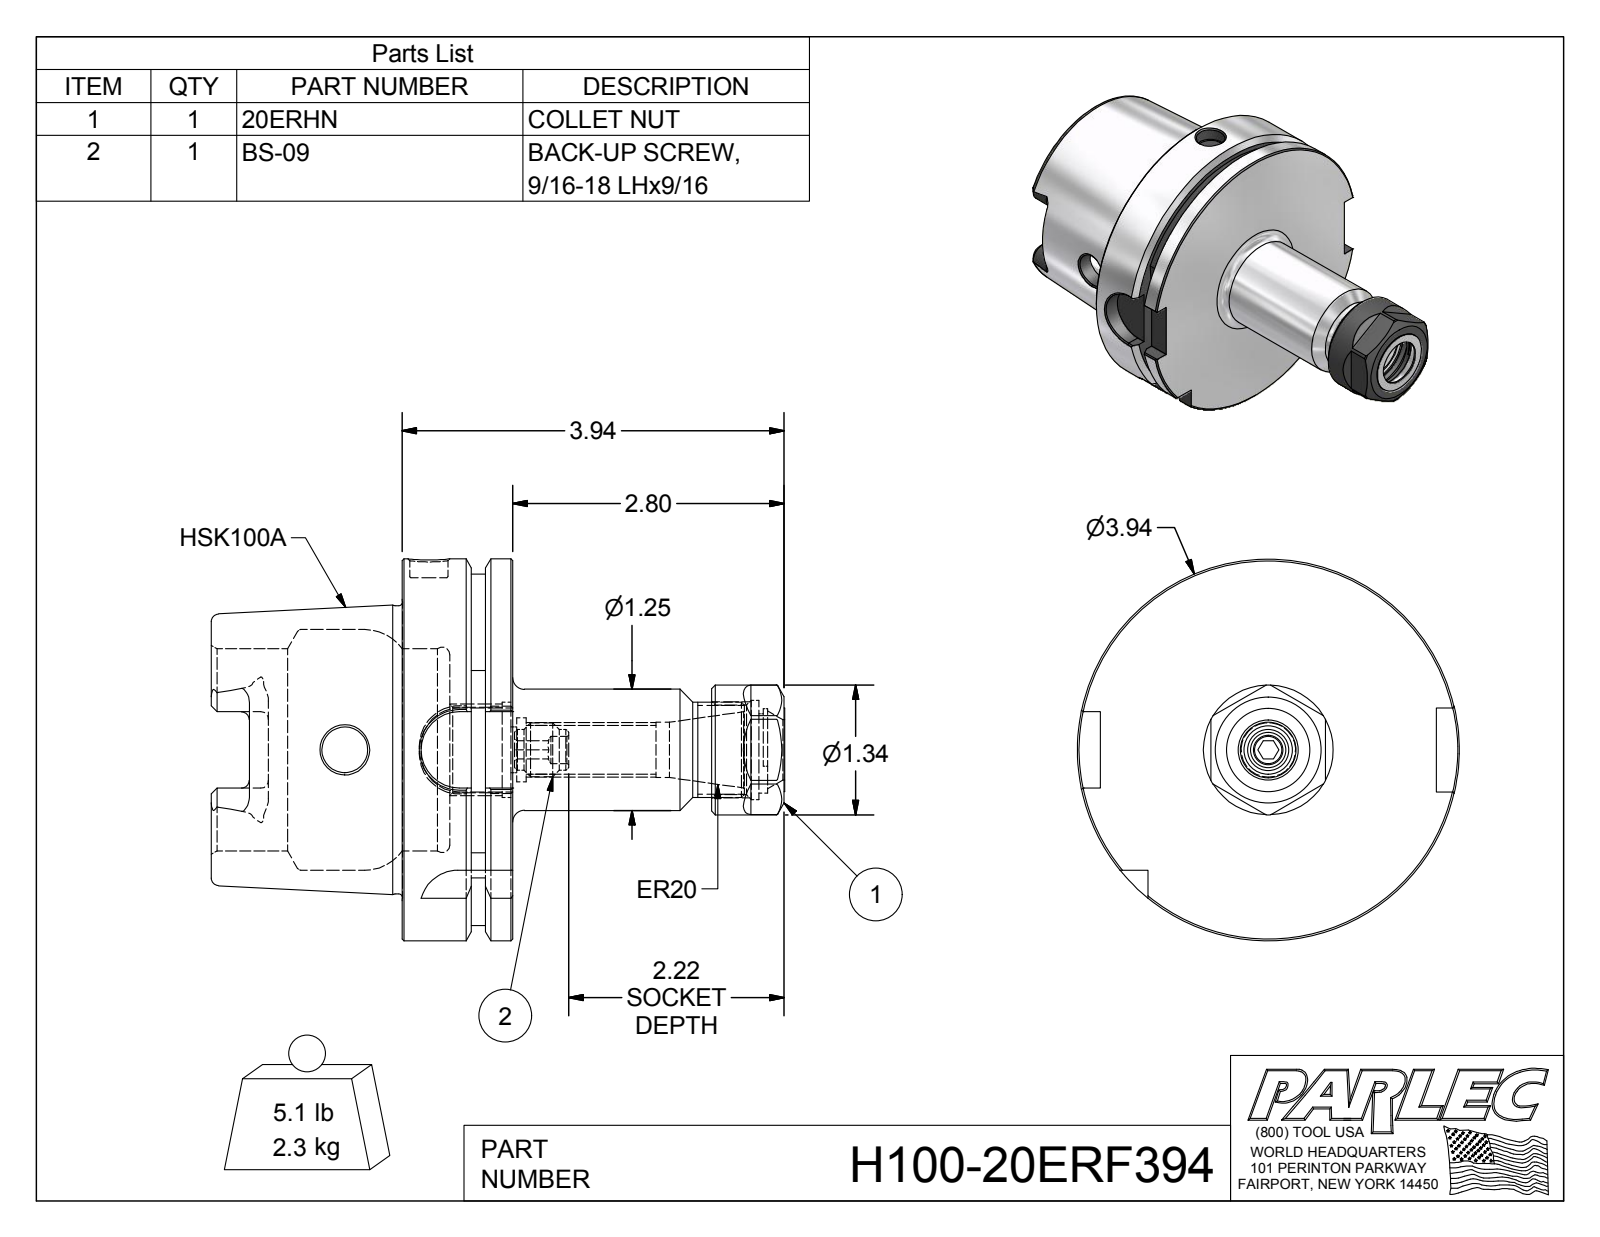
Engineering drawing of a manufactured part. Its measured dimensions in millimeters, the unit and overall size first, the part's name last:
Units: millimetres
Overall size (bounding box): 150.08 × 100 × 100
Round holes (diameter × count): ⌀9 ×2, ⌀12 ×2, ⌀7.14 ×1, ⌀10 ×1, ⌀11.99 ×1, ⌀12.75 ×1, ⌀14.48 ×1, ⌀15.49 ×1, ⌀16.84 ×1, ⌀22.38 ×1, ⌀23.5 ×1, ⌀25.02 ×1
Round bosses / shafts (diameter × count): ⌀100 ×1, ⌀92 ×1, ⌀75.36 ×1, ⌀34 ×1, ⌀31.75 ×1, ⌀25 ×1, ⌀14.1 ×1, ⌀10.72 ×1
Partial cylindrical surfaces — rounded edges, fillets, slot ends (radius × count): R2 ×6, R4.88 ×4, R10 ×4, R9.47 ×1, R10.55 ×1, R10.75 ×1
Main face-to-face distances: 29, 12.5, 16.5, 50, 62.5, 79, 30, 150.08, 100.08, 87.58
Volume: 296 896 mm³ · Surface area: 63 658 mm²
Bodies: 3 solids, 195 faces (75 planar, 50 cylindrical, 70 other)
Part name (STEP PRODUCT): H100-20ER4-1; 20ERHN; BS-09; H100-20ERF394
STEP written by: Autodesk Inventor 2016 (AUTOMOTIVE_DESIGN)
